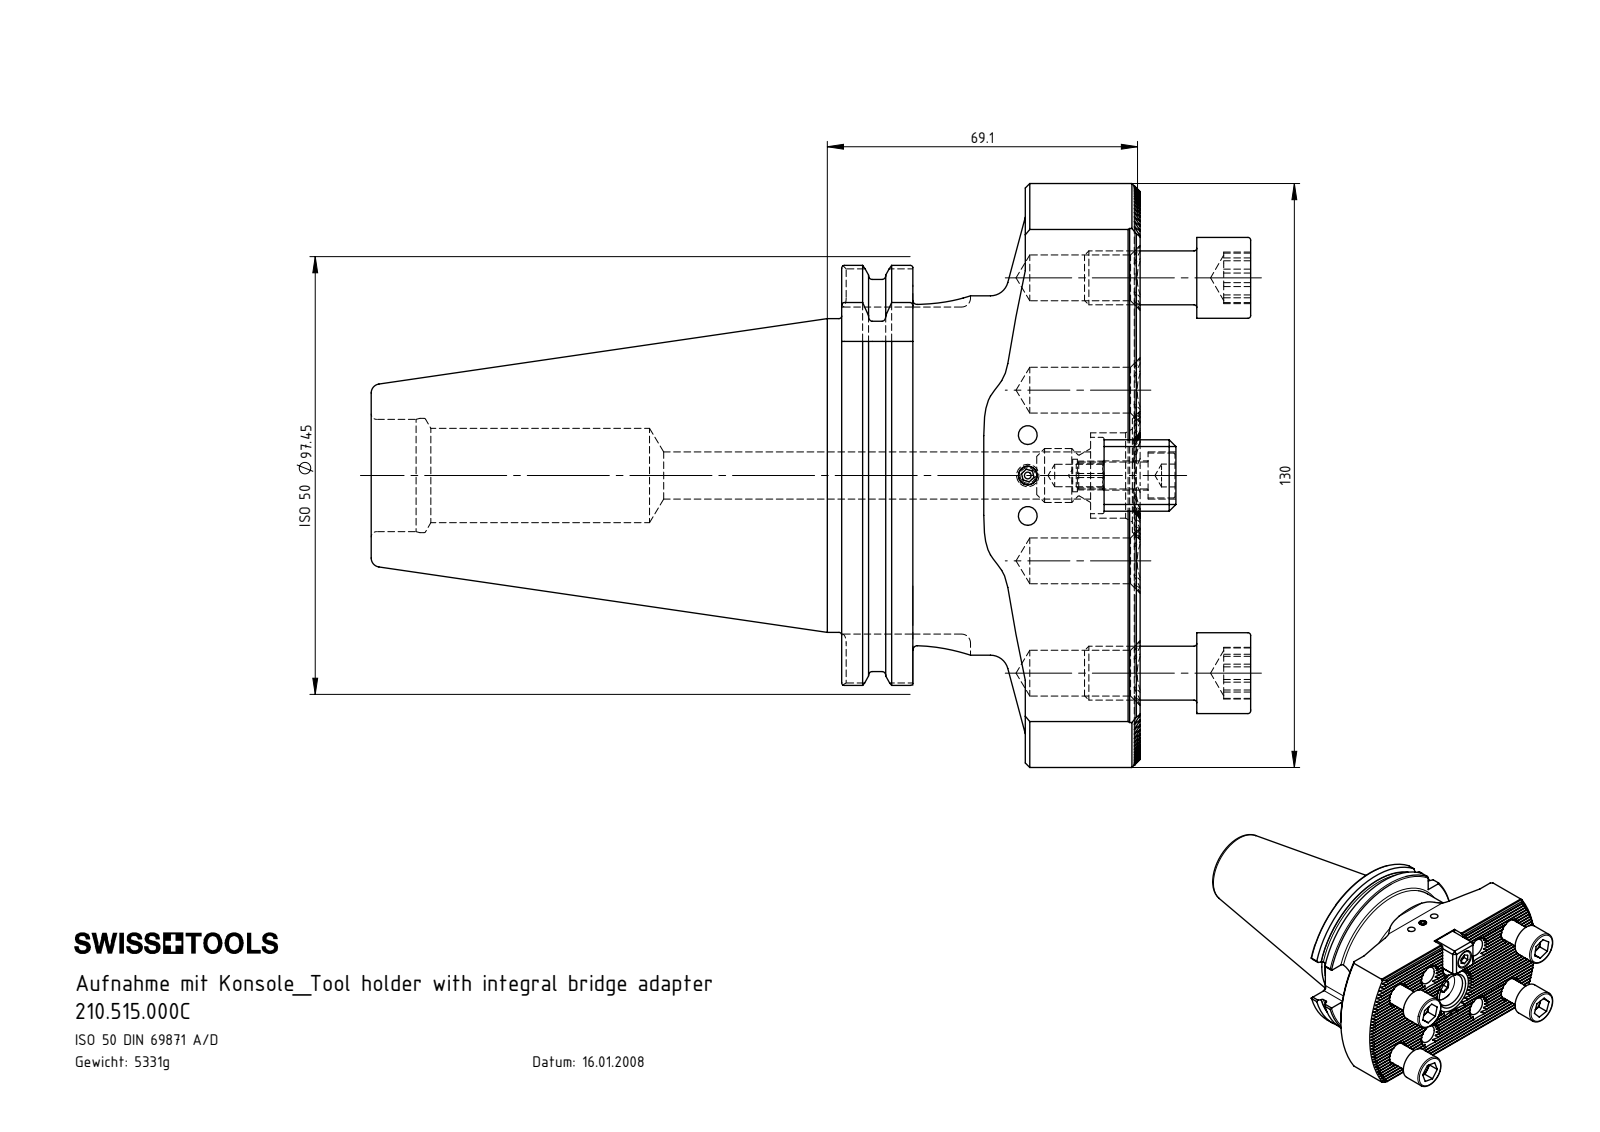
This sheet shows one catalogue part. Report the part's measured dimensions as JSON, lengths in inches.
{"part_name": "210.515.000C; ISO 4026 - M5 x 8_ISO 4026 - M5 x 8; DIN 908 - M12x1.5; ISO 4762 - M12 x 25 (+3 more)", "step_written_by": "SolidWorks 2017 (CONFIG_CONTROL_DESIGN)", "units": "inches", "bodies": {"solids": 10, "faces": 888, "planar": 503, "cylindrical": 213, "other": 172}, "overall_size": [7.713, 5.118, 3.837], "volume_in3": 41.44, "surface_area_in2": 141.8, "round_holes": [[0.402, 8], [0.165, 3], [0.413, 2], [0.059, 1], [0.197, 1], [0.256, 1], [0.285, 1], [0.748, 1], [0.827, 1], [0.984, 1], [1.002, 1]], "round_bosses_or_shafts": [[0.472, 5], [0.709, 4], [3.583, 1], [3.15, 1], [2.75, 1], [0.669, 1], [0.394, 1], [0.236, 1]], "partial_cylinders_radius": [[0.006, 34], [0.079, 8], [0.157, 2], [0.313, 1], [0.506, 1], [1.919, 1], [2.559, 1]], "face_to_face_distances": [0.068, 0.682, 2.756, 0.341, 0.136, 0.205, 0.273, 0.614, 0.75, 0.137], "hole_center_spacings": [0.984, 1.086, 1.575, 1.857, 1.903, 2.48, 2.938, 0.354]}
